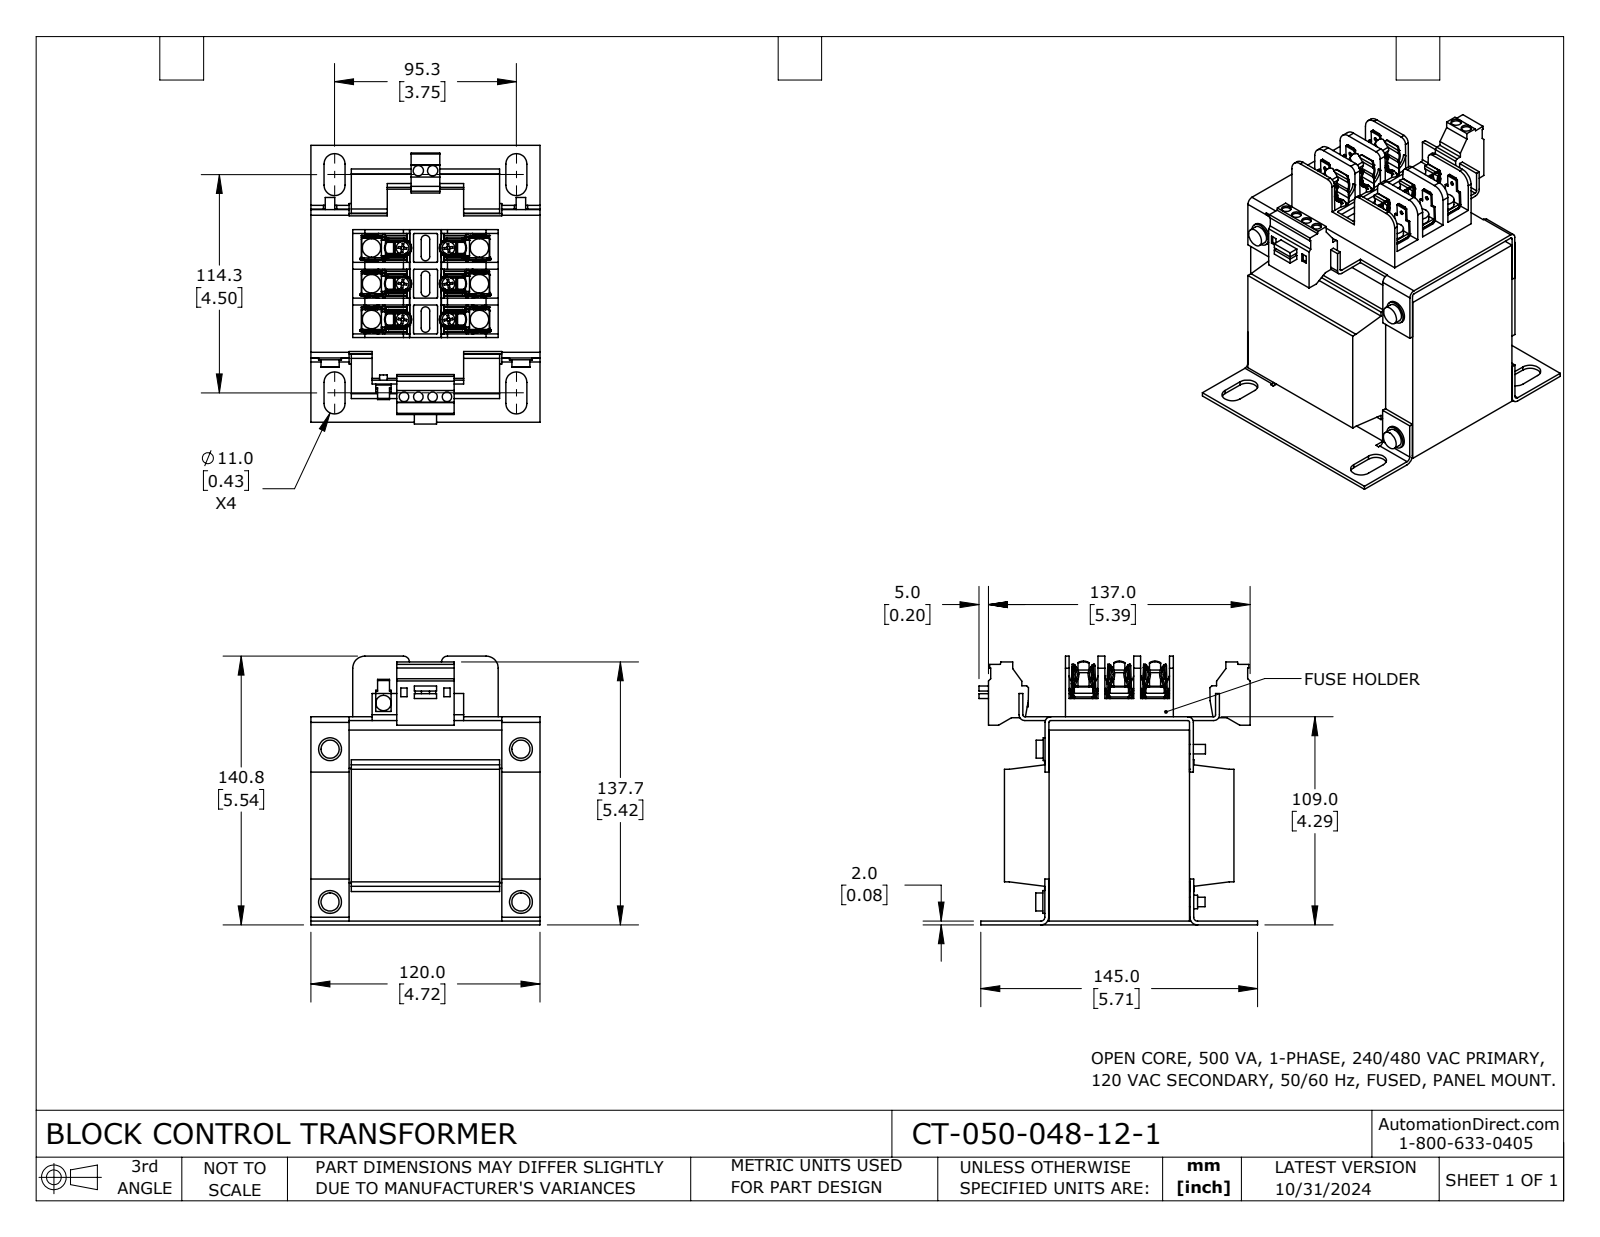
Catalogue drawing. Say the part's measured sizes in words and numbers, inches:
The part is named "CT-050-048-12-1". Its 3-D file was written by "SolidWorks 2023 (CONFIG_CONTROL_DESIGN)". It is 2 solids with 1588 faces: 1027 planar, 531 cylindrical and 30 other. Overall it measures 5.748 by 5.541 by 4.724 inches. Its volume is 75.65 cubic inches and its surface area 300.9 square inches. Round holes: 12 of diameter 0.074, 5 of diameter 0.205, 4 of diameter 0.197, 2 of diameter 0.213, 1 of diameter 0.205. Round bosses or shafts: 6 of diameter 0.38, 6 of diameter 0.19, 4 of diameter 0.472, 4 of diameter 0.374, 4 of diameter 0.236, 4 of diameter 0.197, 2 of diameter 0.276, 1 of diameter 0.315. Partial cylindrical surfaces (rounded edges, fillets, slot ends): 24 of radius 0.01, 20 of radius 0.05, 18 of radius 0.03, 14 of radius 0.072, 12 of radius 0.038, 12 of radius 0.04, 12 of radius 0.164, 9 of radius 0.097. The main face-to-face distances are 0.079, 4.213, 3.937, 0.787, 0.833, 3.892, 4.291, 3.15, 0.197, 4.134. The hole center spacings are 2.232, 2.354, 0.026, 0.026, 0.052, 0.295, 0.738, 1.863.
